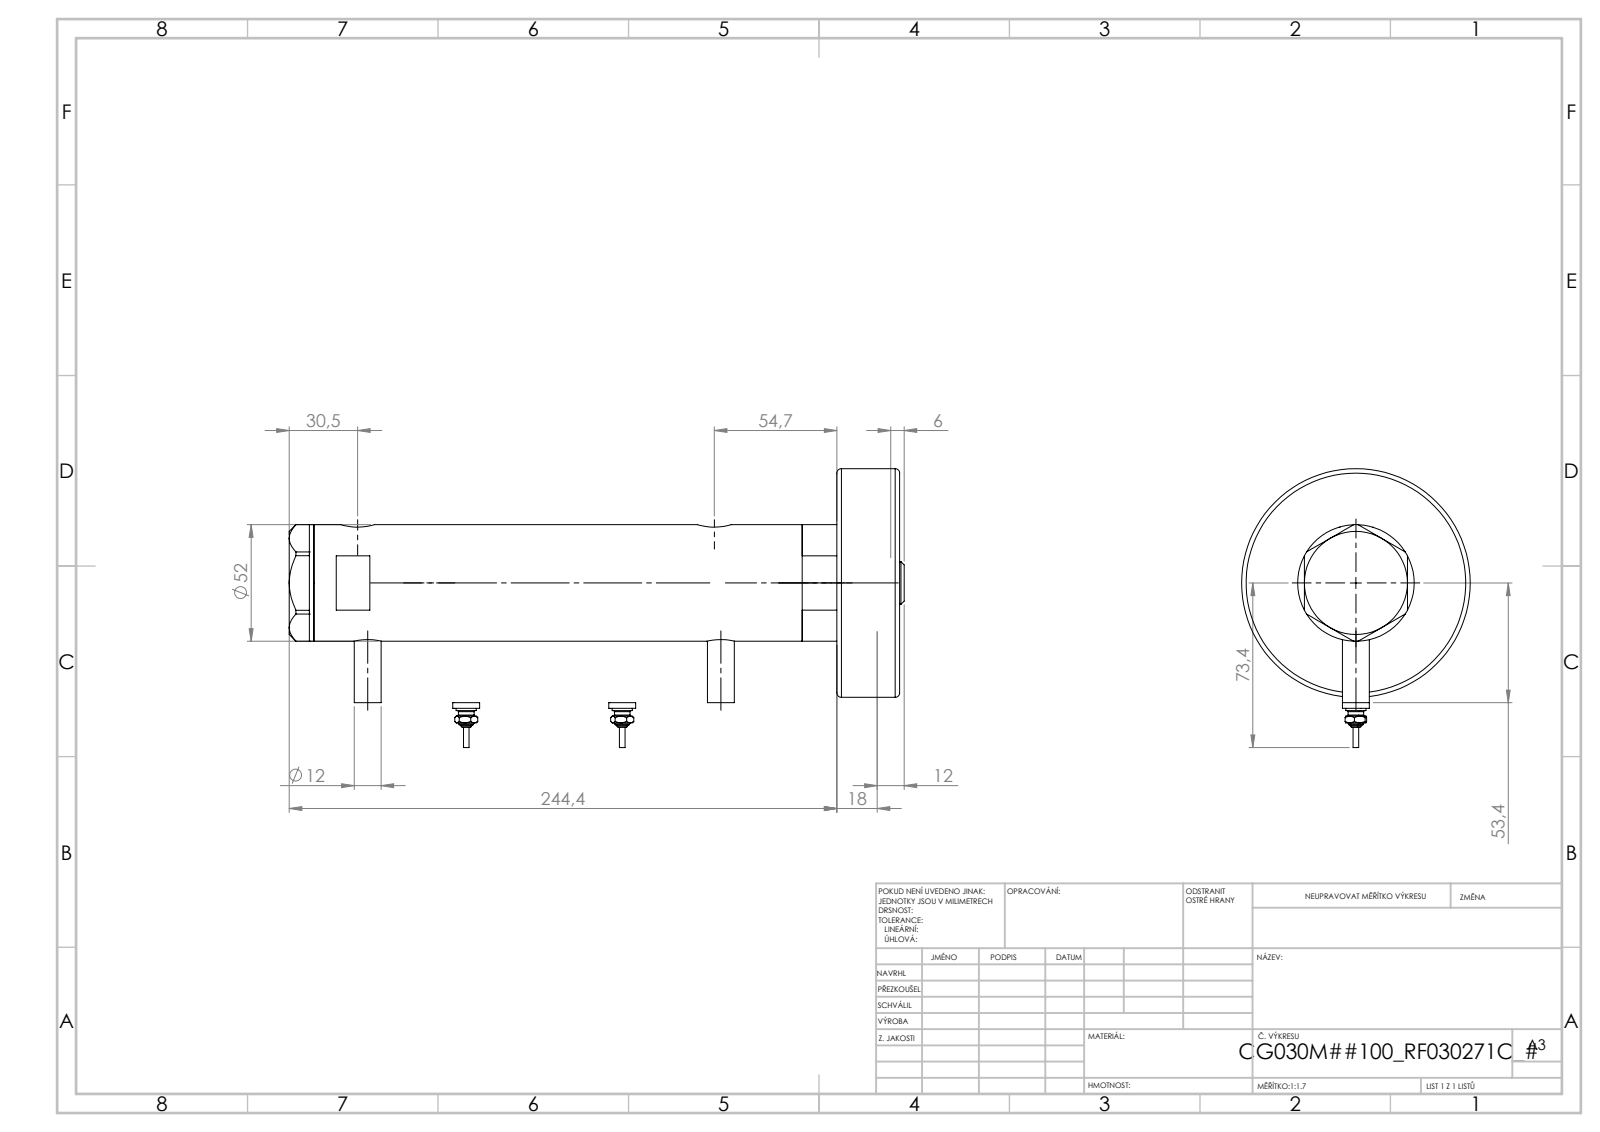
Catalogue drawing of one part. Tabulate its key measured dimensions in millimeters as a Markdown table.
| quantity | value |
| --- | --- |
| part name | V270CG_MIDDLE; V270CG_BACK; V270CG_VC; V270CG_FRONT (+1 more) |
| STEP written by | SolidWorks 2019 (CONFIG_CONTROL_DESIGN) |
| units | millimeters |
| bodies | 6 solids, 246 faces (95 planar, 77 cylindrical, 74 other) |
| overall size | 249.02 × 84.3 × 52 |
| volume | 443 477 mm³ |
| surface area | 99 080 mm² |
| round holes (diameter × count) | 5 × 2, 9.73 × 2, 12.5 × 2, 15 × 2, 6.5 × 1, 20 × 1, 21.5 × 1, 30 × 1, 33 × 1, 44 × 1 |
| round bosses / shafts (diameter × count) | 12 × 3, 9 × 2, 7 × 2, 4.34 × 2, 2.4 × 2, 52 × 1, 40 × 1, 38 × 1 |
| main face-to-face distances | 153.54, 23.8, 129.74, 11, 34.8, 164.54, 46, 200.94, 189.94, 166.14 |
| hole center spacings | 2.9, 4.5, 126.75, 129.65, 131.25, 134.15, 2.89, 2.91 |
